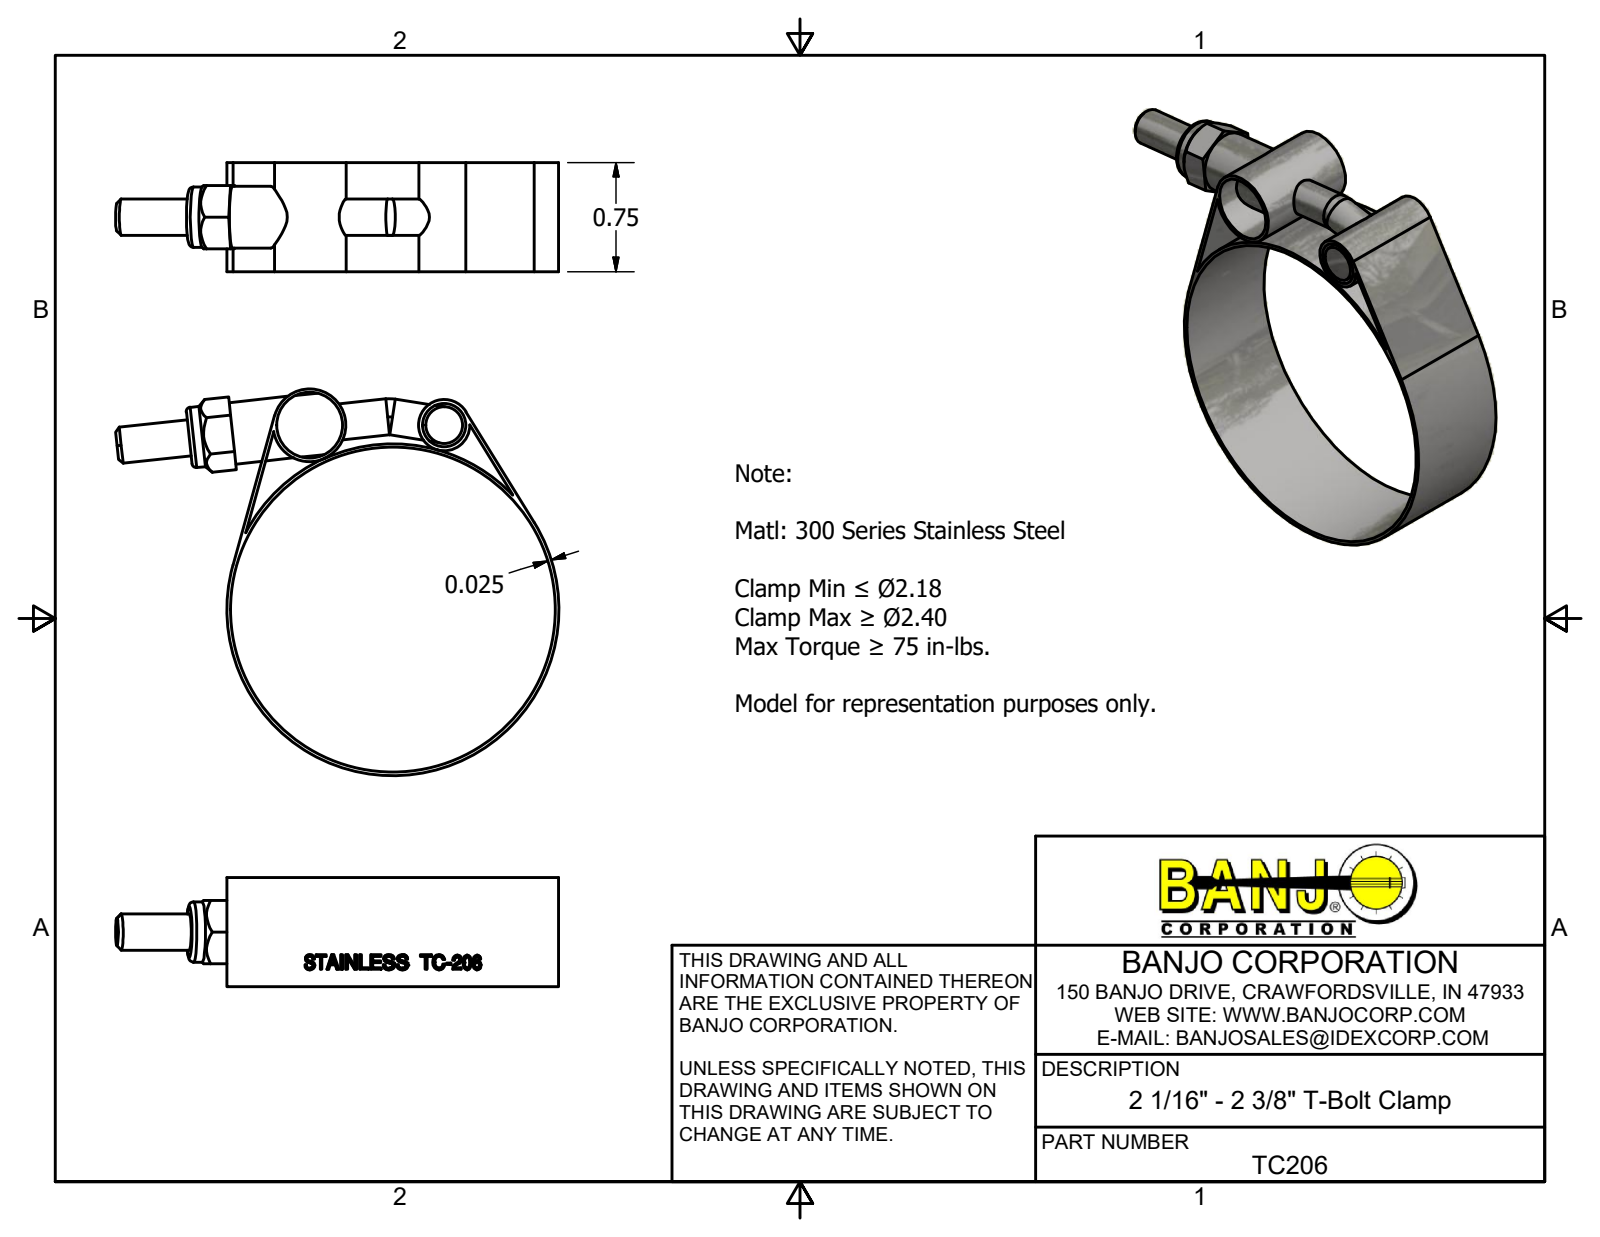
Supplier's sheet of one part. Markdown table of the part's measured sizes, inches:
| quantity | value |
| --- | --- |
| part name | TC206 |
| STEP written by | Autodesk Inventor 2018 (AUTOMOTIVE_DESIGN) |
| units | inches |
| bodies | 1 solid, 234 faces (87 planar, 34 cylindrical, 113 other) |
| overall size | 3.047 × 2.657 × 0.75 |
| volume | 0.439 in³ |
| surface area | 19.48 in² |
| round holes (diameter × count) | 0.3 × 1, 0.45 × 1, 2.23 × 1 |
| round bosses / shafts (diameter × count) | 2.28 × 1, 0.5 × 1, 0.425 × 1, 0.415 × 1, 0.35 × 1, 0.25 × 1 |
| partial cylindrical surfaces (radius × count) | 1.135 × 1 |
| main face-to-face distances | 0.025, 0.75, 0.435, 0.157, 0.592, 0.435, 0.5, 0.8, 0.3, 0.039 |
| hole center spacings | 0.925, 1.315, 1.39 |
